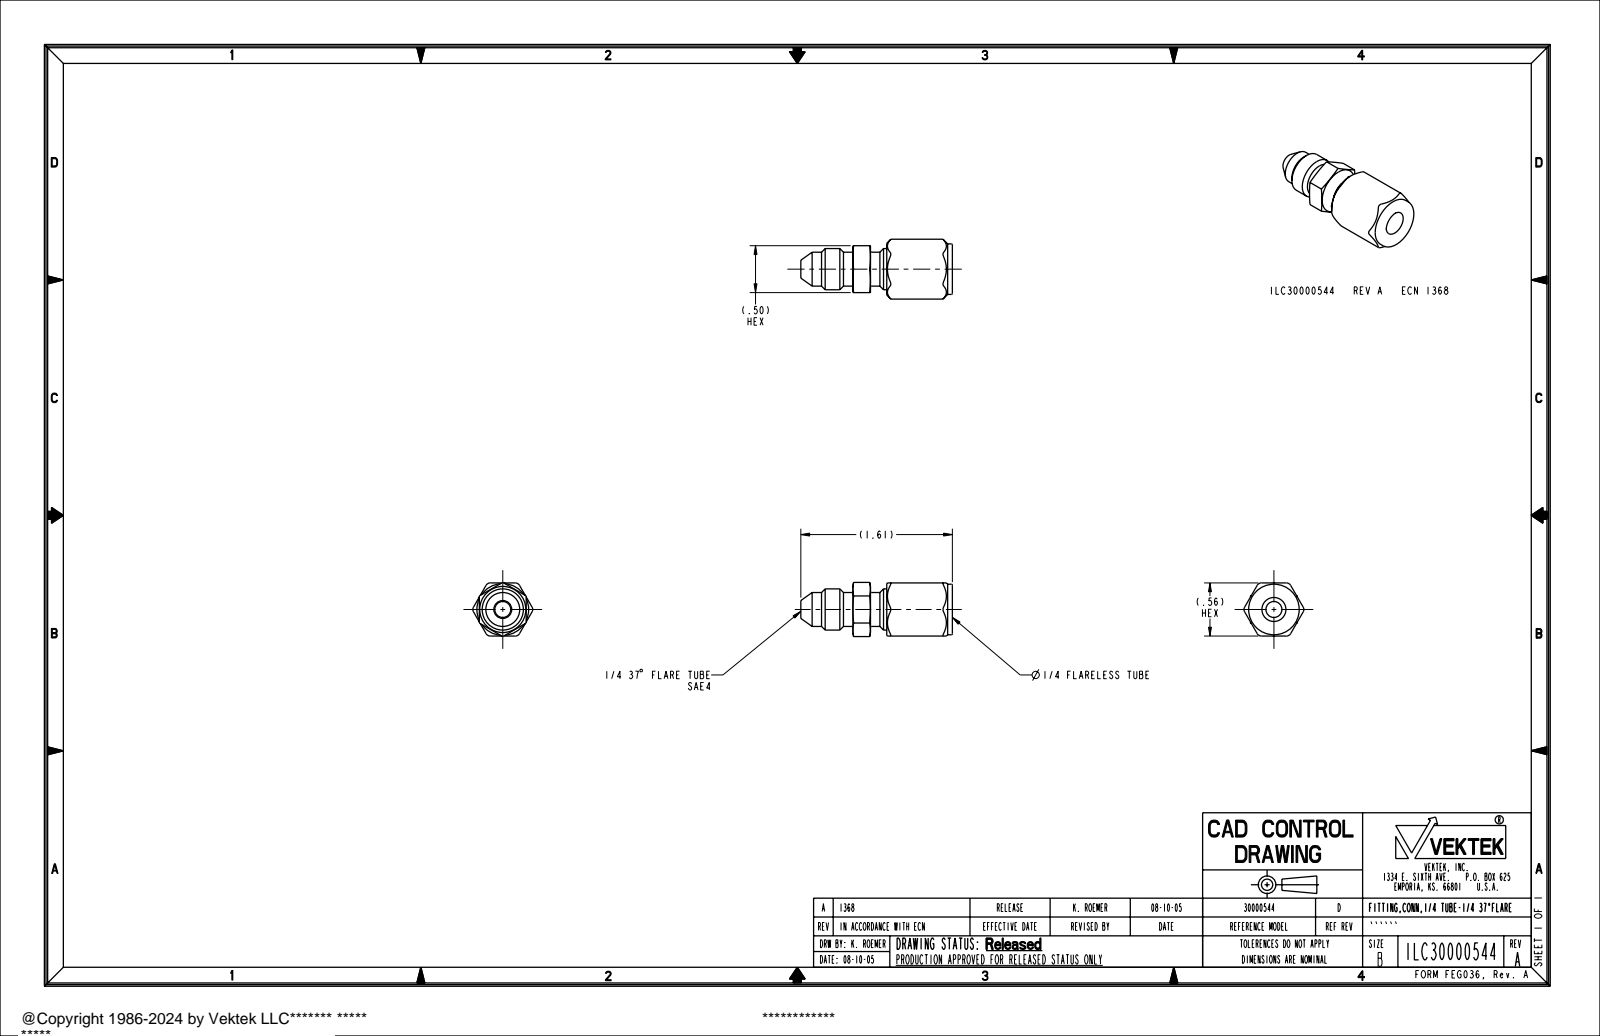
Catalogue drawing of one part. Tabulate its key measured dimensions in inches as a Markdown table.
| quantity | value |
| --- | --- |
| part name | ILC30000544 |
| STEP written by | PRO/ENGINEER BY PARAMETRIC TECHNOLOGY CORPORATION, 2004290 (AUTOMOTIVE_DESIGN_CC2) |
| units | inches |
| bodies | 1 solid, 66 faces (18 planar, 22 cylindrical, 26 other) |
| overall size | 1.61 × 0.636 × 0.575 |
| volume | 0.253 in³ |
| surface area | 4.13 in² |
| round holes (diameter × count) | 0.17 × 1, 0.255 × 1 |
| round bosses / shafts (diameter × count) | 0.537 × 1, 0.437 × 1, 0.36 × 1 |
| partial cylindrical surfaces (radius × count) | 0.05 × 6 |
| main face-to-face distances | 0.564, 0.498, 0.697, 0.87, 1.057, 0.173, 0.36, 0.187, 0.66, 0.037 |
